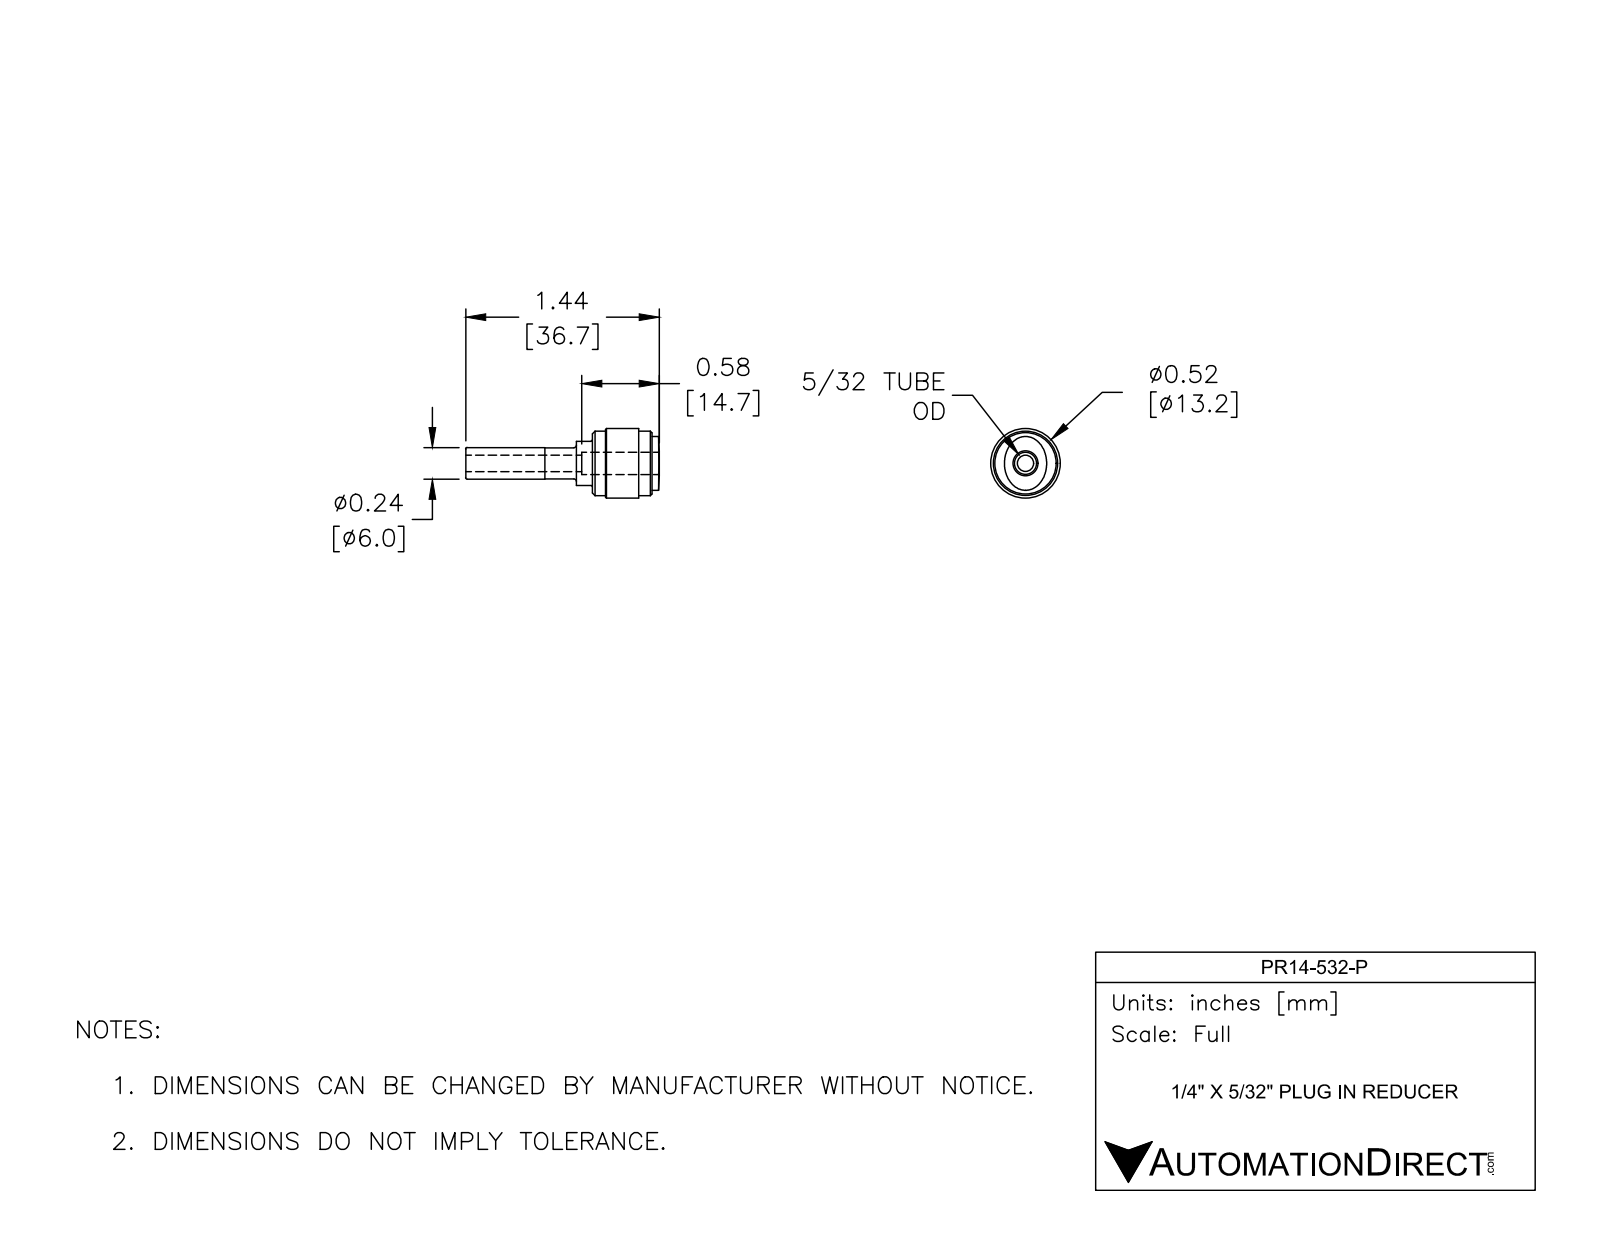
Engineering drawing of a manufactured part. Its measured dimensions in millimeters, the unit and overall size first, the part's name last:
Units: millimetres
Overall size (bounding box): 36.7 × 13.2 × 13.2
Round holes (diameter × count): ⌀3.1 ×1, ⌀4.2 ×1
Round bosses / shafts (diameter × count): ⌀13.2 ×1, ⌀12.2 ×1, ⌀8.4 ×1, ⌀6 ×1, ⌀5.9 ×1
Main face-to-face distances: 11.3, 2.5, 8.8, 3, 11.8, 14.3, 21, 24, 32.8, 35.3
Volume: 1 920 mm³ · Surface area: 1 599 mm²
Bodies: 1 solid, 43 faces (9 planar, 16 cylindrical, 18 other)
Part name (STEP PRODUCT): PR14-532-P
STEP written by: SolidWorks 2017 (AUTOMOTIVE_DESIGN)
